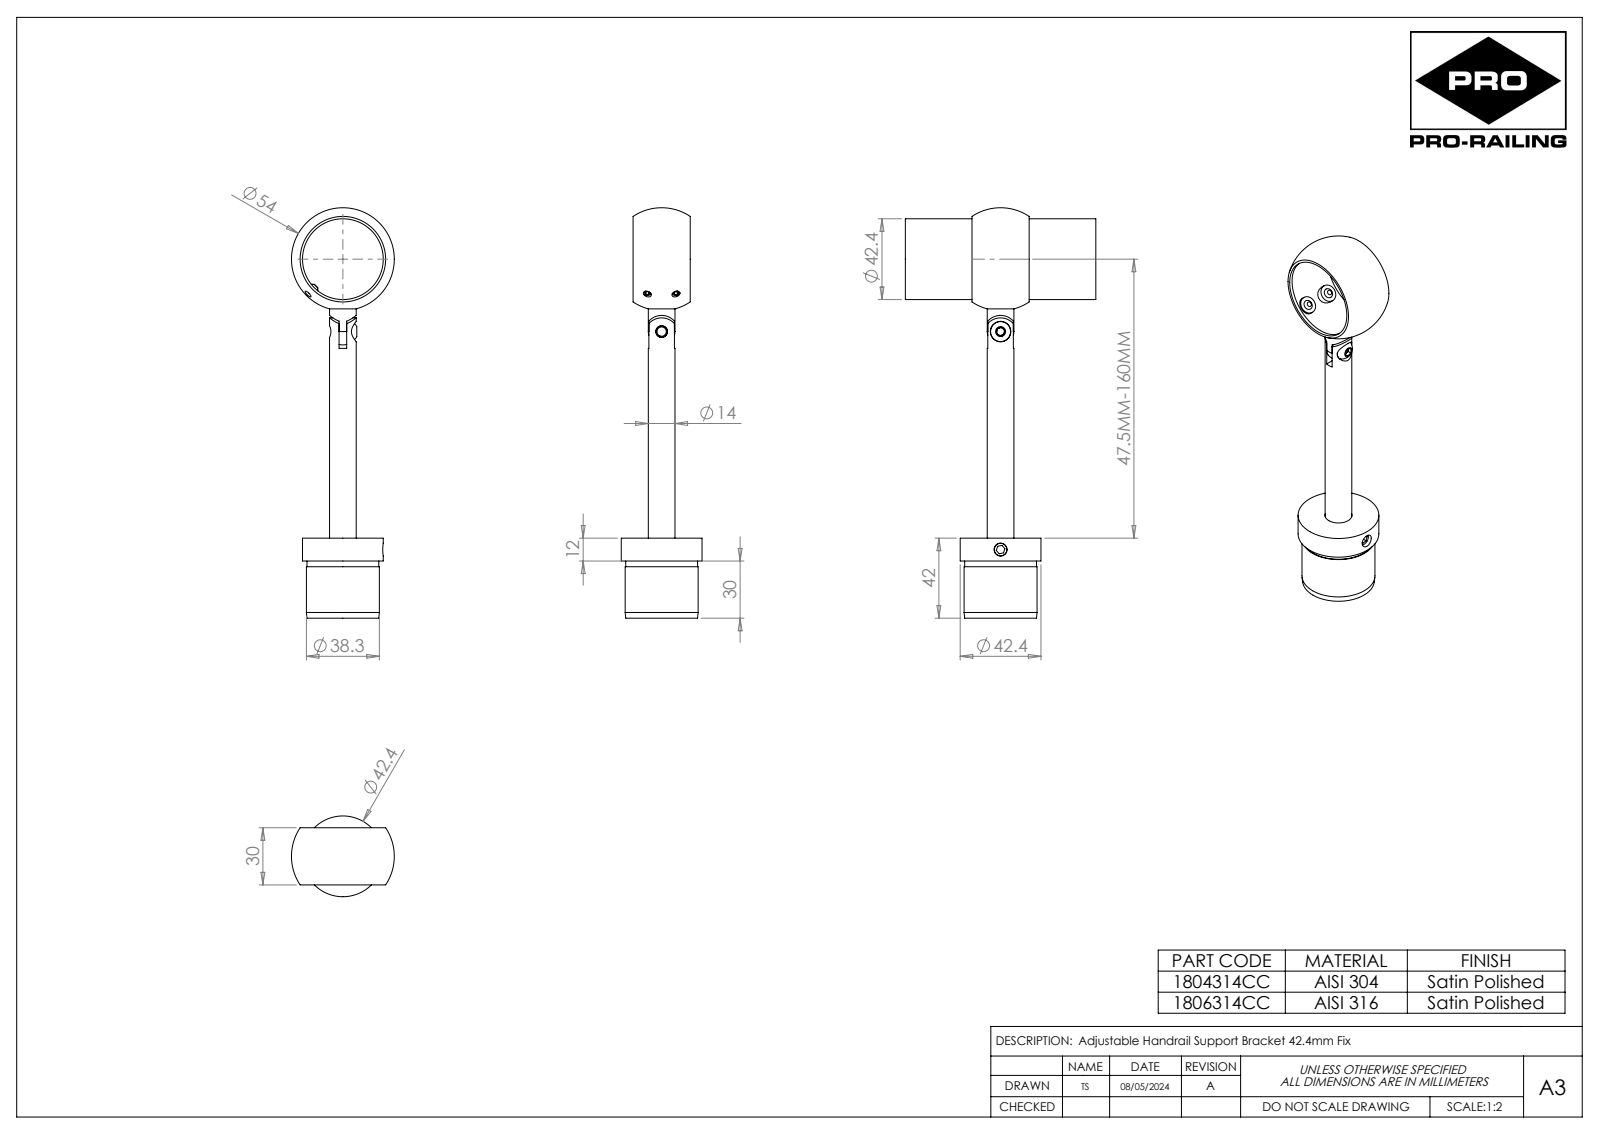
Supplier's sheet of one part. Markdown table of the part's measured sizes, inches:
| quantity | value |
| --- | --- |
| part name | 1804314CC CUS |
| STEP written by | SolidWorks 2023 (CONFIG_CONTROL_DESIGN) |
| units | inches |
| bodies | 7 solids, 172 faces (69 planar, 65 cylindrical, 38 other) |
| overall size | 8.48 × 2.126 × 1.669 |
| volume | 3.229 in³ |
| surface area | 52.89 in² |
| round holes (diameter × count) | 0.165 × 2, 0.197 × 1, 0.244 × 1, 0.268 × 1, 0.425 × 1, 0.559 × 1, 1.35 × 1, 1.669 × 1 |
| round bosses / shafts (diameter × count) | 0.354 × 2, 0.197 × 2, 1.669 × 1, 1.508 × 1, 1.484 × 1, 0.787 × 1, 0.551 × 1, 0.413 × 1 |
| partial cylindrical surfaces (radius × count) | 0.039 × 10, 0.354 × 2, 0.197 × 1 |
| main face-to-face distances | 0.157, 1.181, 0.472, 0.315, 0.118, 1.496, 1.654, 0.709, 1.024, 0.645 |
| hole center spacings | 0.591, 4.504 |
